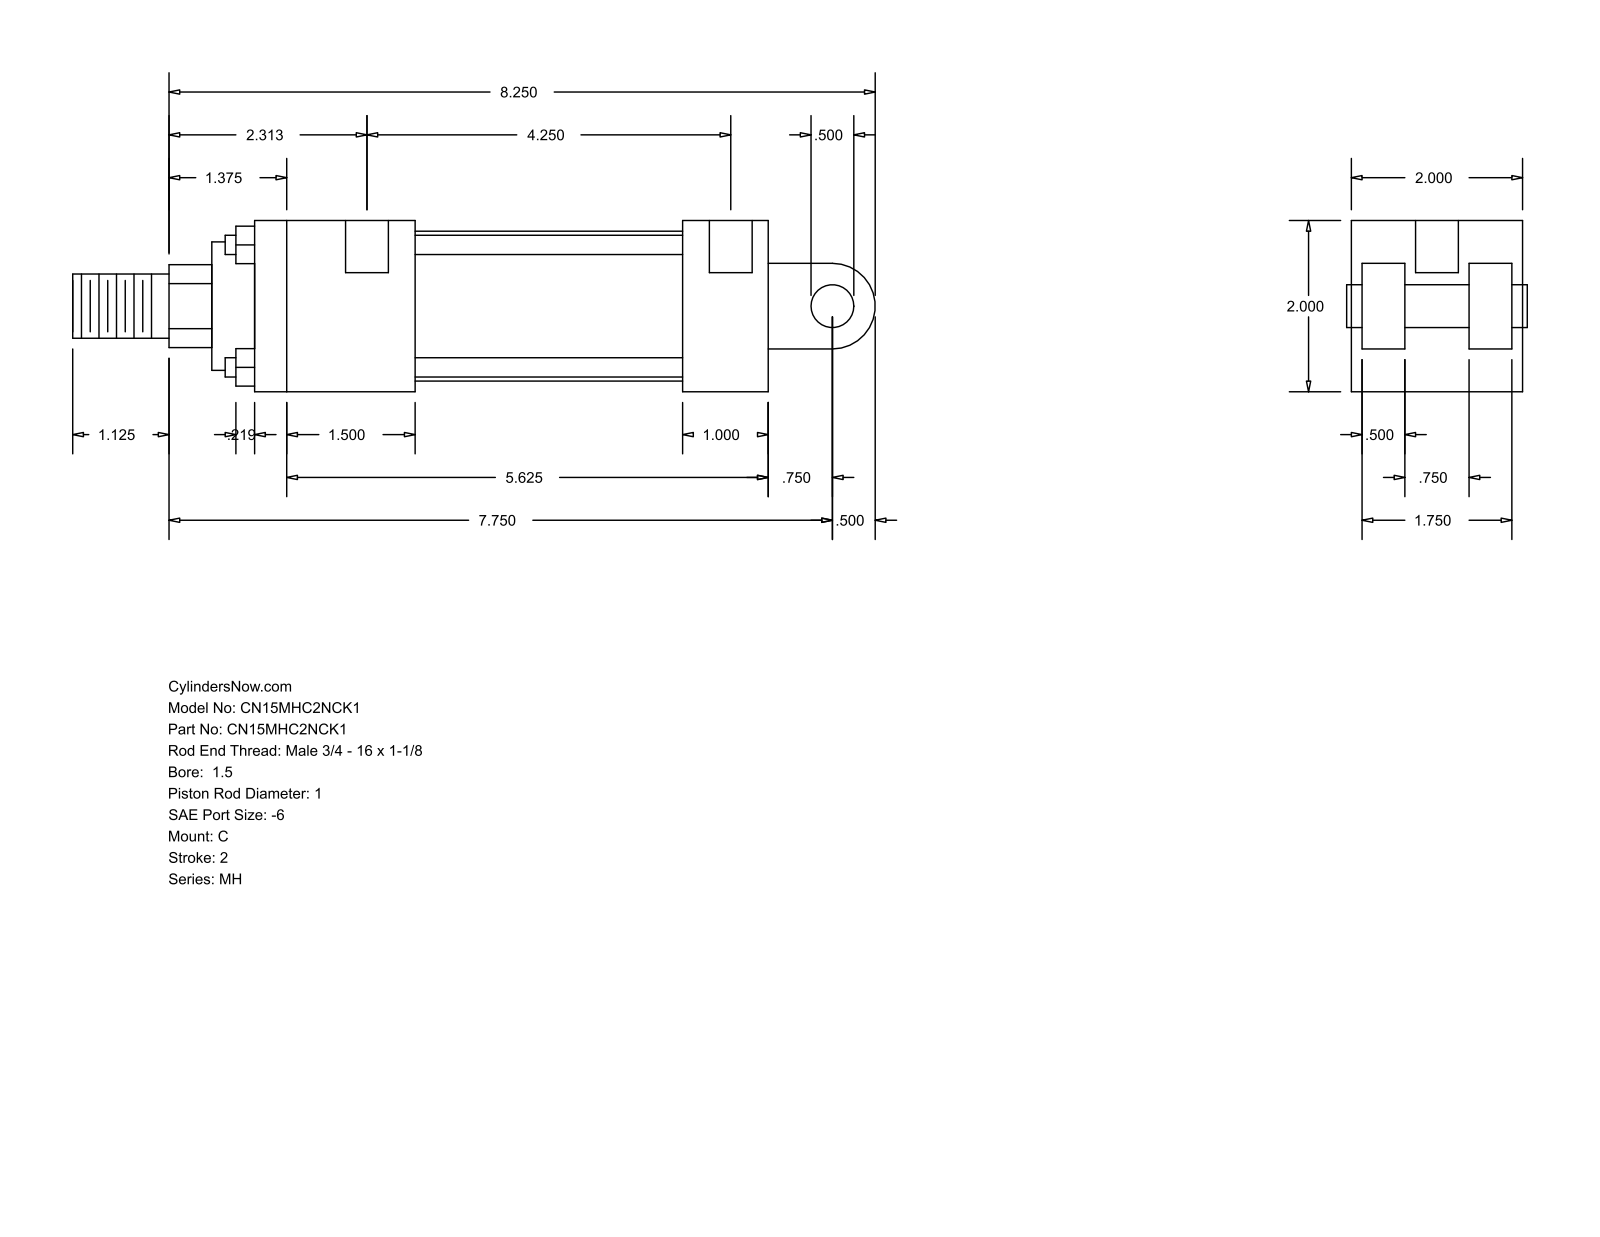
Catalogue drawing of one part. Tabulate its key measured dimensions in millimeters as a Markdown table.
| quantity | value |
| --- | --- |
| part name | MH_C__0150_1 |
| STEP written by | GSSL Pune (CONFIG_CONTROL_DESIGN) |
| units | millimeters |
| bodies | 0 solids, 99 faces (70 planar, 29 cylindrical, 0 other) |
| overall size | 238.12 × 50.8 × 50.8 |
| round holes (diameter × count) | 5.56 × 4, 12.7 × 2 |
| round bosses / shafts (diameter × count) | 5.71 × 4, 44.45 × 1, 38.1 × 1, 25.4 × 1, 19.05 × 1, 12.7 × 1 |
| partial cylindrical surfaces (radius × count) | 12.29 × 1, 12.7 × 1 |
| main face-to-face distances | 50.8, 12.7, 47.63, 25.4, 3.17, 15.87, 34.93, 31.76, 152.4, 38.1 |
| hole center spacings | 111.13, 3.18, 107.95 |
